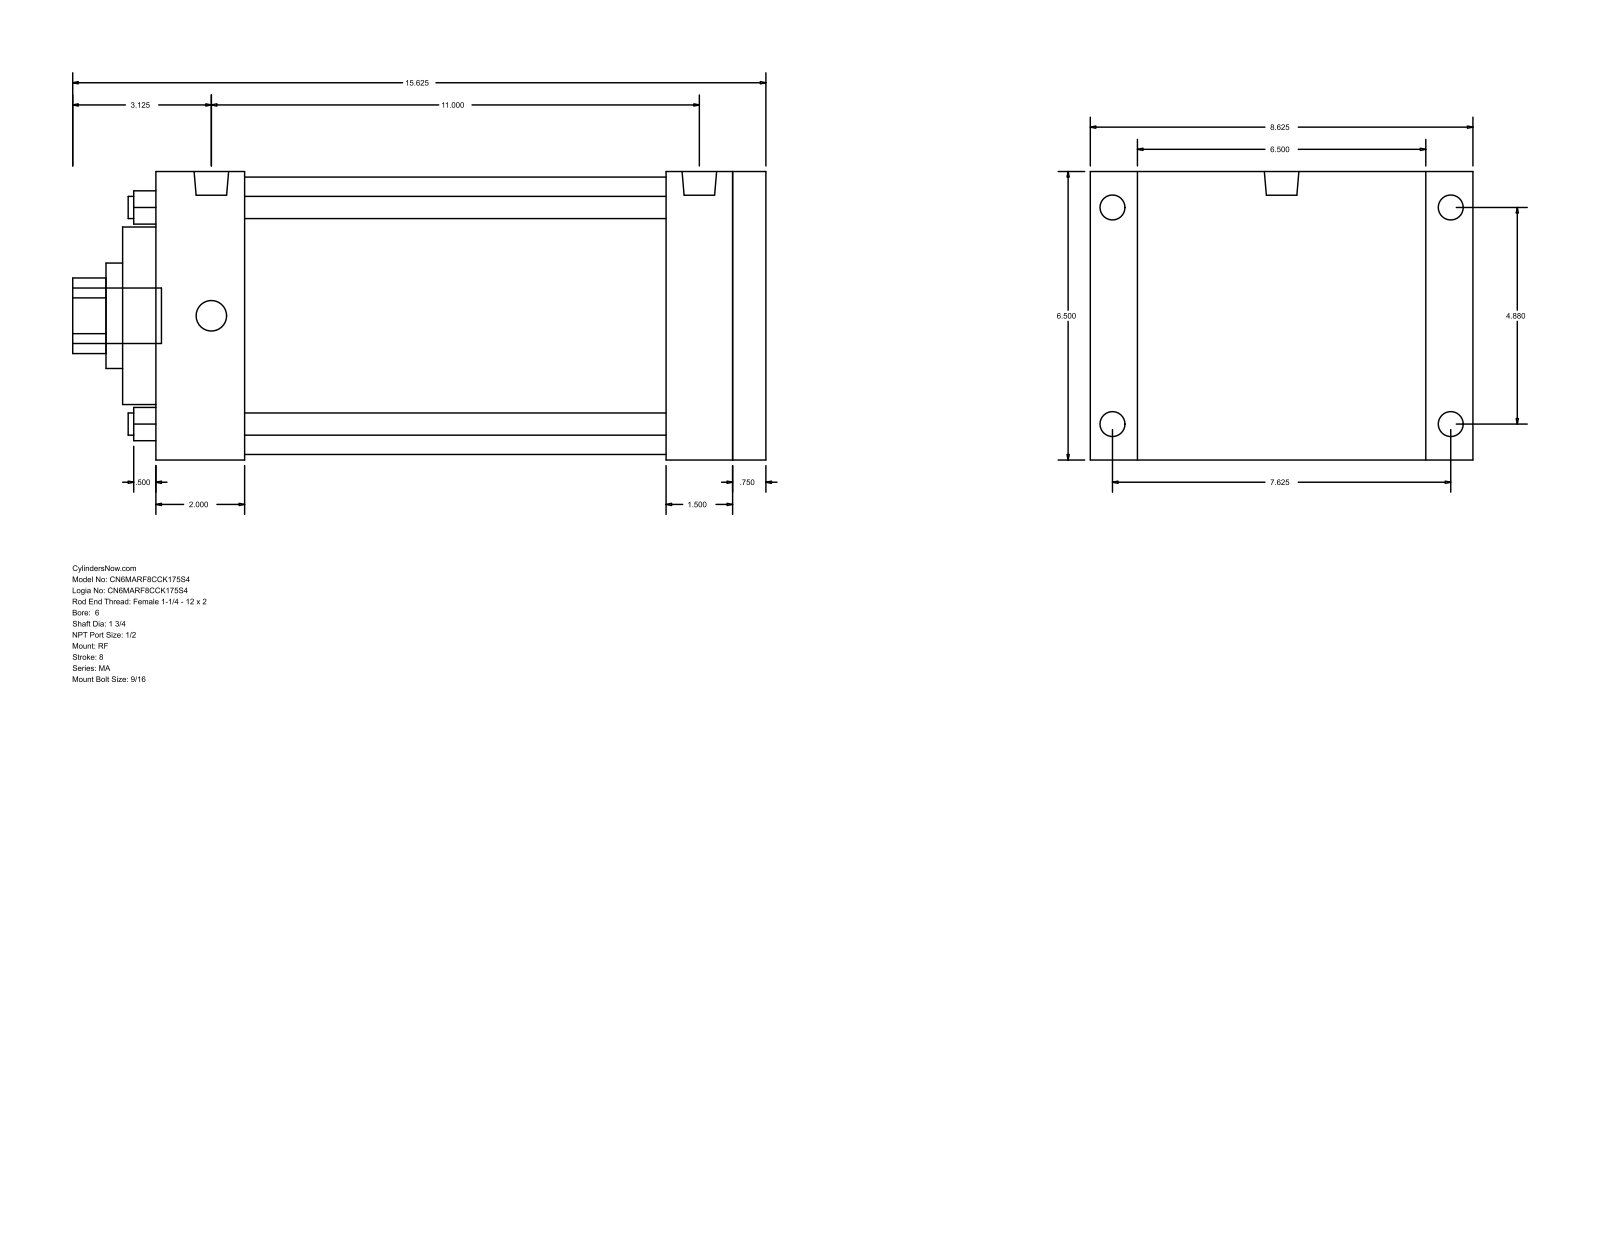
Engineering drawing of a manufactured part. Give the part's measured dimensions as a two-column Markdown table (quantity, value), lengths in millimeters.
| quantity | value |
| --- | --- |
| part name | MA_RF__0600_1.75 |
| STEP written by | GSSL Pune (CONFIG_CONTROL_DESIGN) |
| units | millimeters |
| bodies | 0 solids, 94 faces (65 planar, 29 cylindrical, 0 other) |
| overall size | 396.88 × 219.07 × 165.1 |
| round holes (diameter × count) | 12.7 × 4, 44.45 × 1, 60.33 × 1, 101.6 × 1, 158.75 × 1 |
| round bosses / shafts (diameter × count) | 17.46 × 4, 14.29 × 4, 19.77 × 2, 31.75 × 1 |
| partial cylindrical surfaces (radius × count) | 21.63 × 1 |
| main face-to-face distances | 165.1, 349.26, 330.2, 19.06, 19.05, 50.8, 279.4, 298.46, 292.11, 241.31 |
| hole center spacings | 87.65, 123.96, 175.31 |
